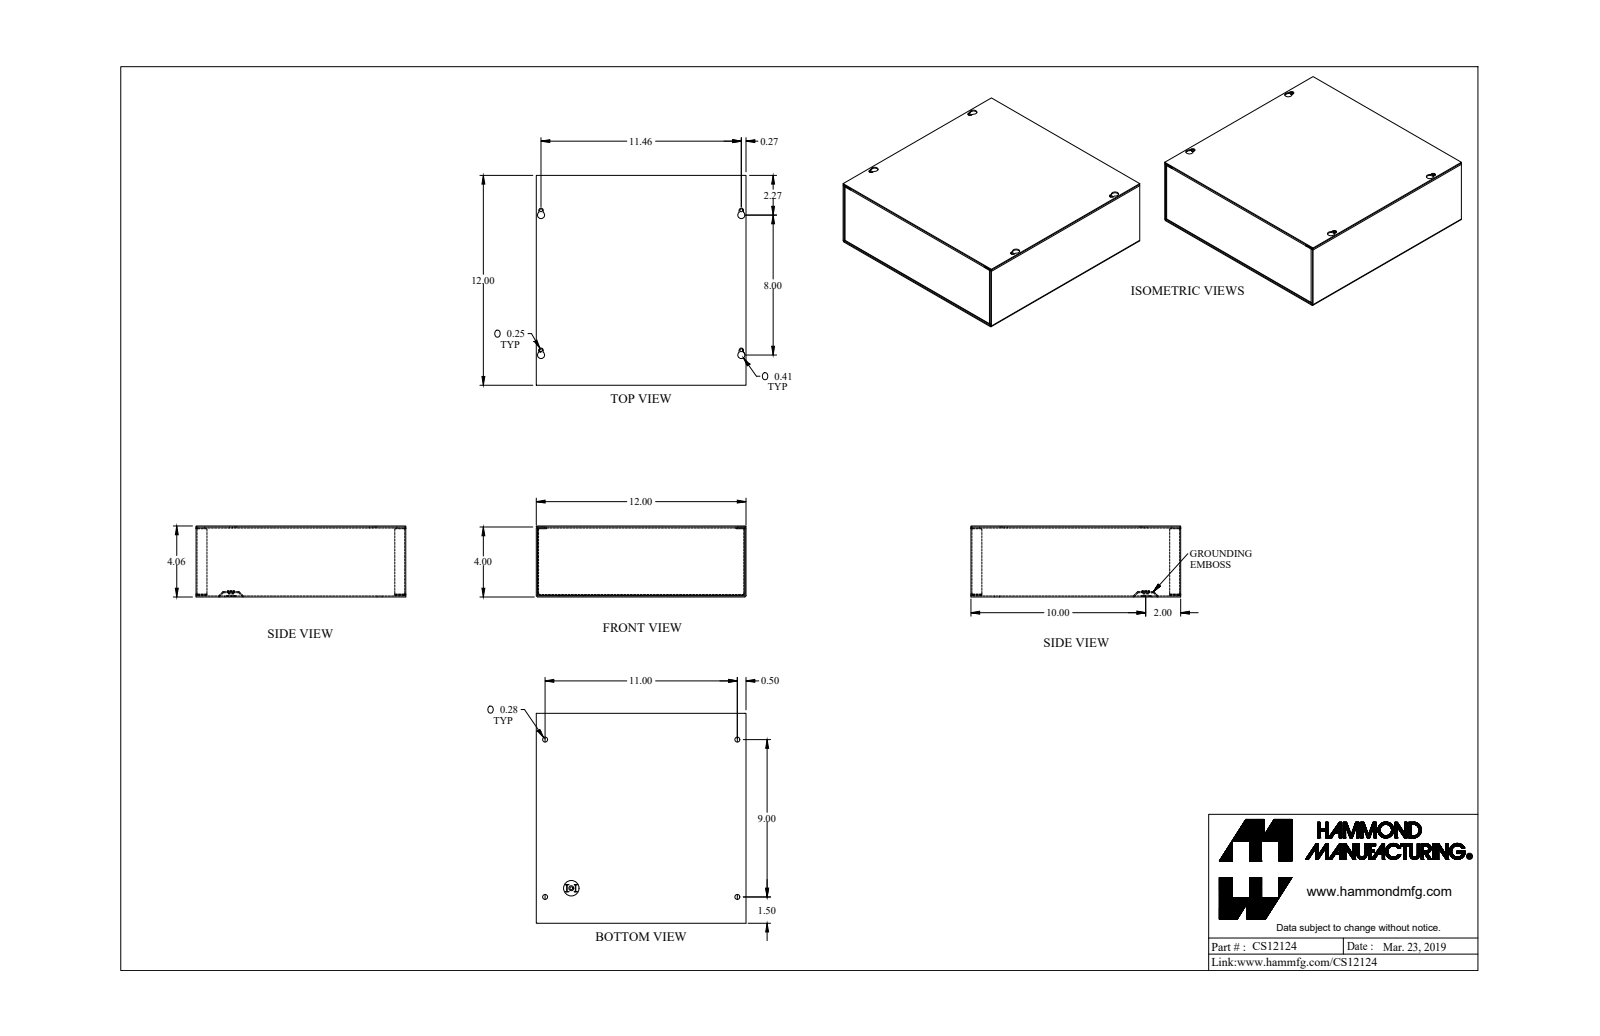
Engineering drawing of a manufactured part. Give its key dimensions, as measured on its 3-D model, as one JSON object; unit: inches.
{"part_name": "CS12124_Default", "step_written_by": "SolidWorks 2019 (CONFIG_CONTROL_DESIGN)", "units": "inches", "bodies": {"solids": 4, "faces": 205, "planar": 125, "cylindrical": 72, "other": 8}, "overall_size": [12, 12, 4.057], "volume_in3": 29.31, "surface_area_in2": 1040, "round_holes": [[0.17, 5], [0.281, 4], [0.5, 1]], "round_bosses_or_shafts": [[0.492, 1], [0.284, 1]], "partial_cylinders_radius": [[0.029, 12], [0.086, 12], [0.057, 8], [0.125, 4], [0.203, 4]], "face_to_face_distances": [0.057, 4, 11.943, 3.943, 4.057, 12, 11.886, 0.08, 3.863, 3.92], "hole_center_spacings": [0.55, 8.503, 11.241, 14.084, 8, 9, 11, 11.46]}
